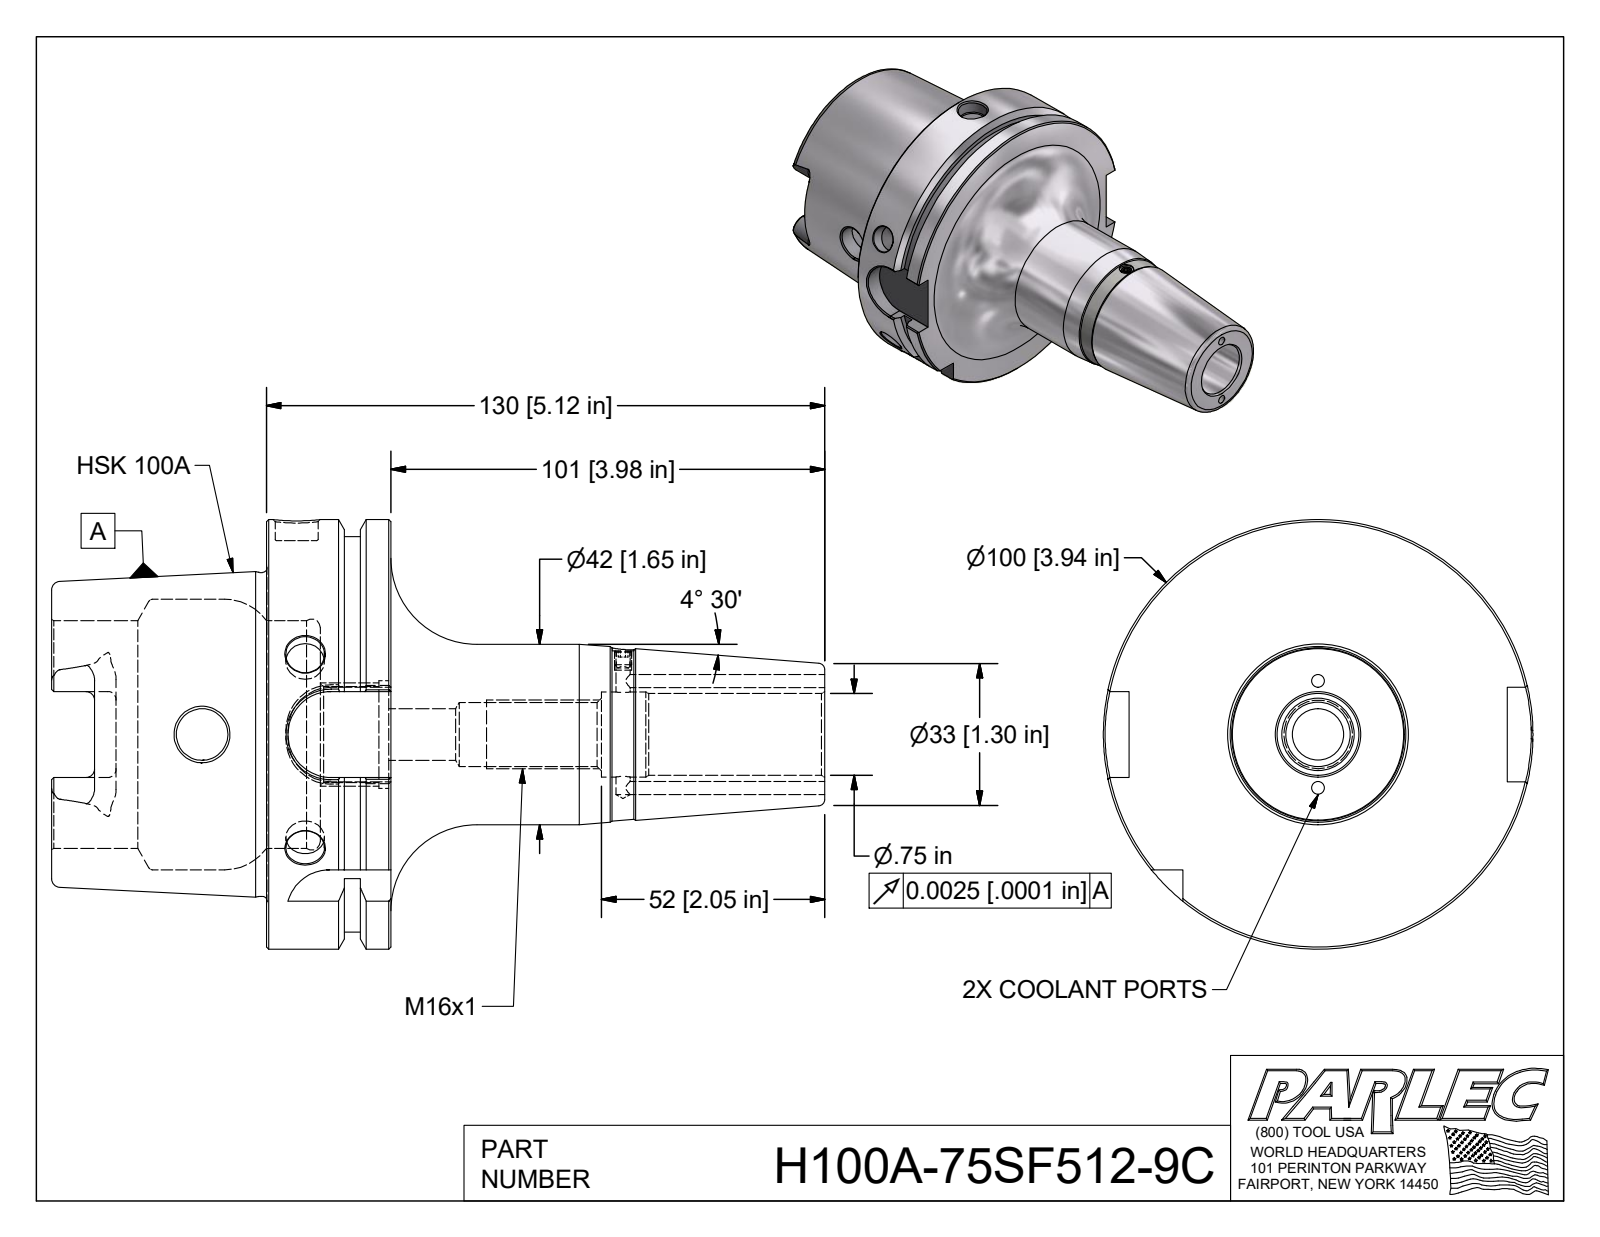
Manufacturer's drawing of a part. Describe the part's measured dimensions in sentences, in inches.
Its 3-D file was written by "Autodesk Inventor 2018 (AUTOMOTIVE_DESIGN)". It is 1 solid with 153 faces: 49 planar, 42 cylindrical and 62 other. Overall it measures 7.087 by 3.937 by 3.937 inches. Its volume is 22.46 cubic inches and its surface area 103.9 square inches. Round holes: 2 of diameter 0.118, 2 of diameter 0.354, 2 of diameter 0.472, 1 of diameter 0.128, 1 of diameter 0.197, 1 of diameter 0.394, 1 of diameter 0.587, 1 of diameter 0.749, 1 of diameter 0.779, 1 of diameter 0.881, 1 of diameter 0.985, 1 of diameter 2.087. Round bosses or shafts: 1 of diameter 3.937, 1 of diameter 3.622, 1 of diameter 2.967, 1 of diameter 1.654. Partial cylindrical surfaces (rounded edges, fillets, slot ends): 6 of radius 0.079, 4 of radius 0.192, 4 of radius 0.394. The main face-to-face distances are 1.142, 0.492, 0.65, 1.969, 2.461, 3.11, 3.465, 2.83, 0.861, 0.369. The hole center spacings are 0.49, 0.98, 2.993.
